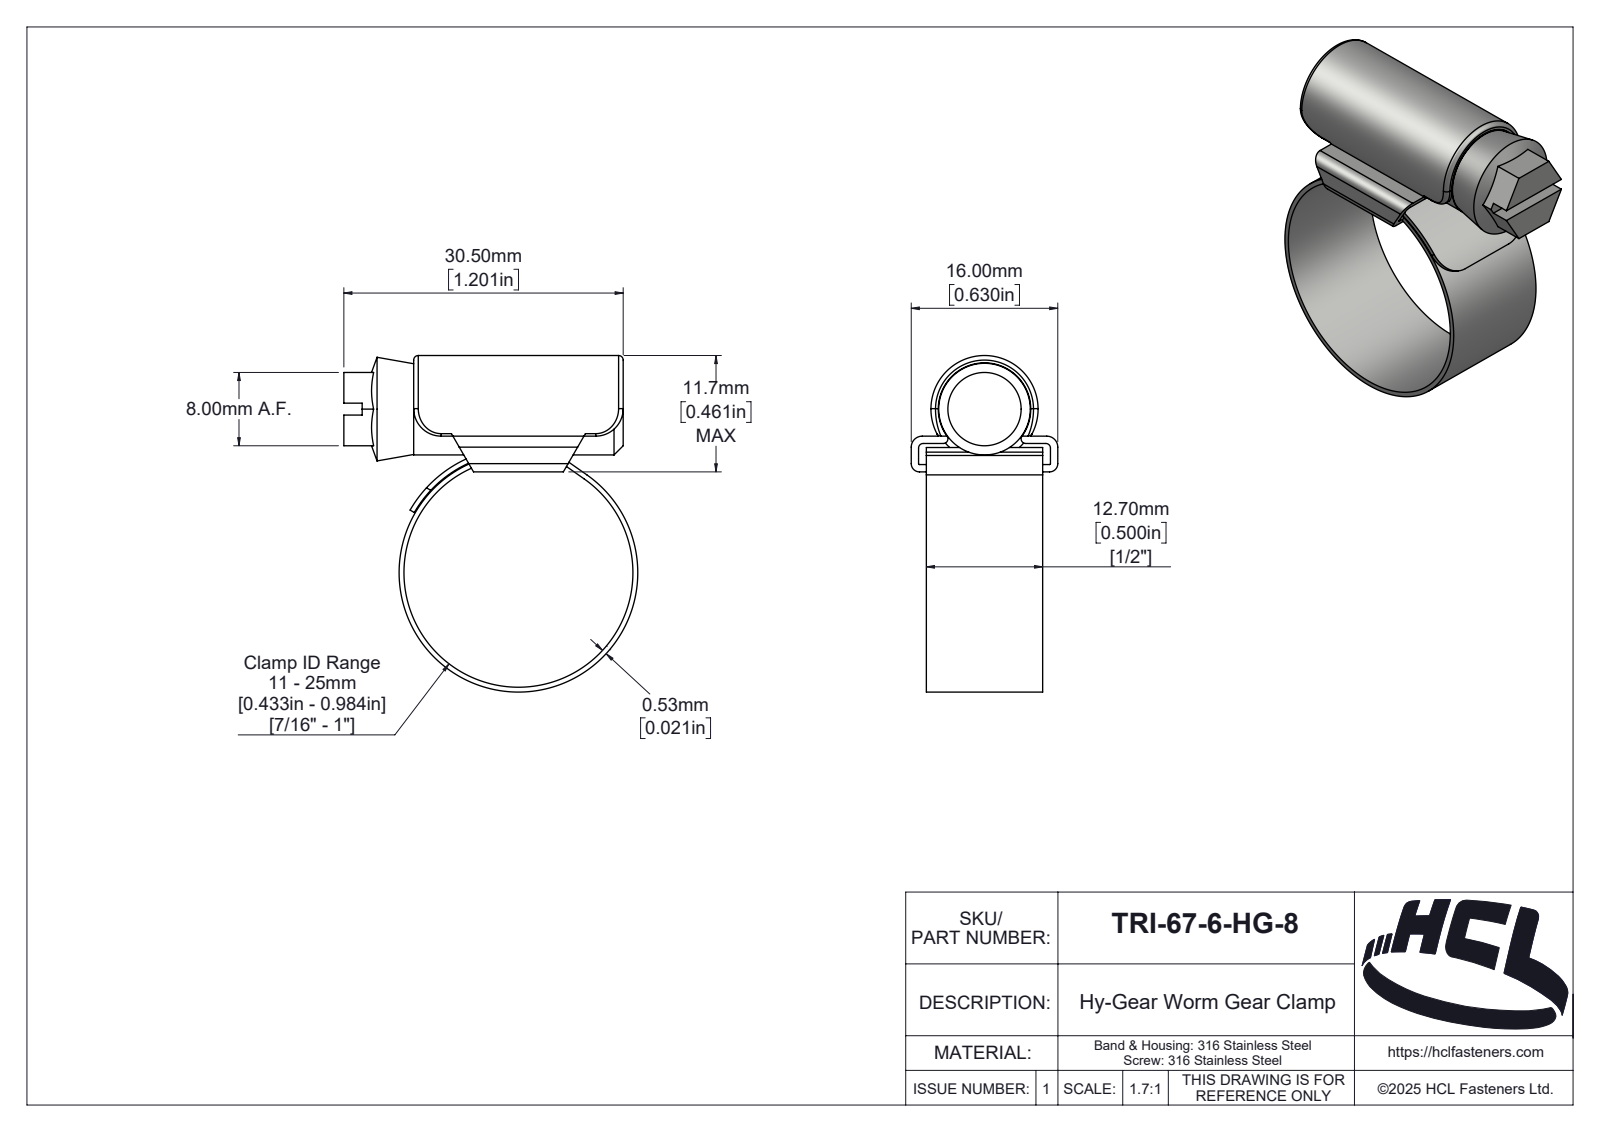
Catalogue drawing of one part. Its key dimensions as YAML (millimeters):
part_name: "TRI-57-0-HG-8"
step_written_by: "SolidWorks 2025 (AUTOMOTIVE_DESIGN)"
units: millimeters
bodies: {solids: 3, faces: 189, planar: 39, cylindrical: 89, other: 61}
overall_size: [36.73, 32.09, 16]
volume: 3627
surface_area: 5405
round_holes:
  - {diameter: 25, count: 1}
round_bosses_or_shafts:
  - {diameter: 26.06, count: 1}
  - {diameter: 10, count: 1}
partial_cylinders:
  - {radius: 0.5, count: 6}
  - {radius: 3, count: 4}
  - {radius: 0.1, count: 2}
  - {radius: 0.9, count: 2}
  - {radius: 1.2, count: 2}
  - {radius: 0.46, count: 1}
  - {radius: 1.89, count: 1}
  - {radius: 2, count: 1}
face_to_face_distances: [0.8, 3.1, 2.3, 3.9, 12.7, 0.53, 30.5, 1.65, 14.35, 15.2]
